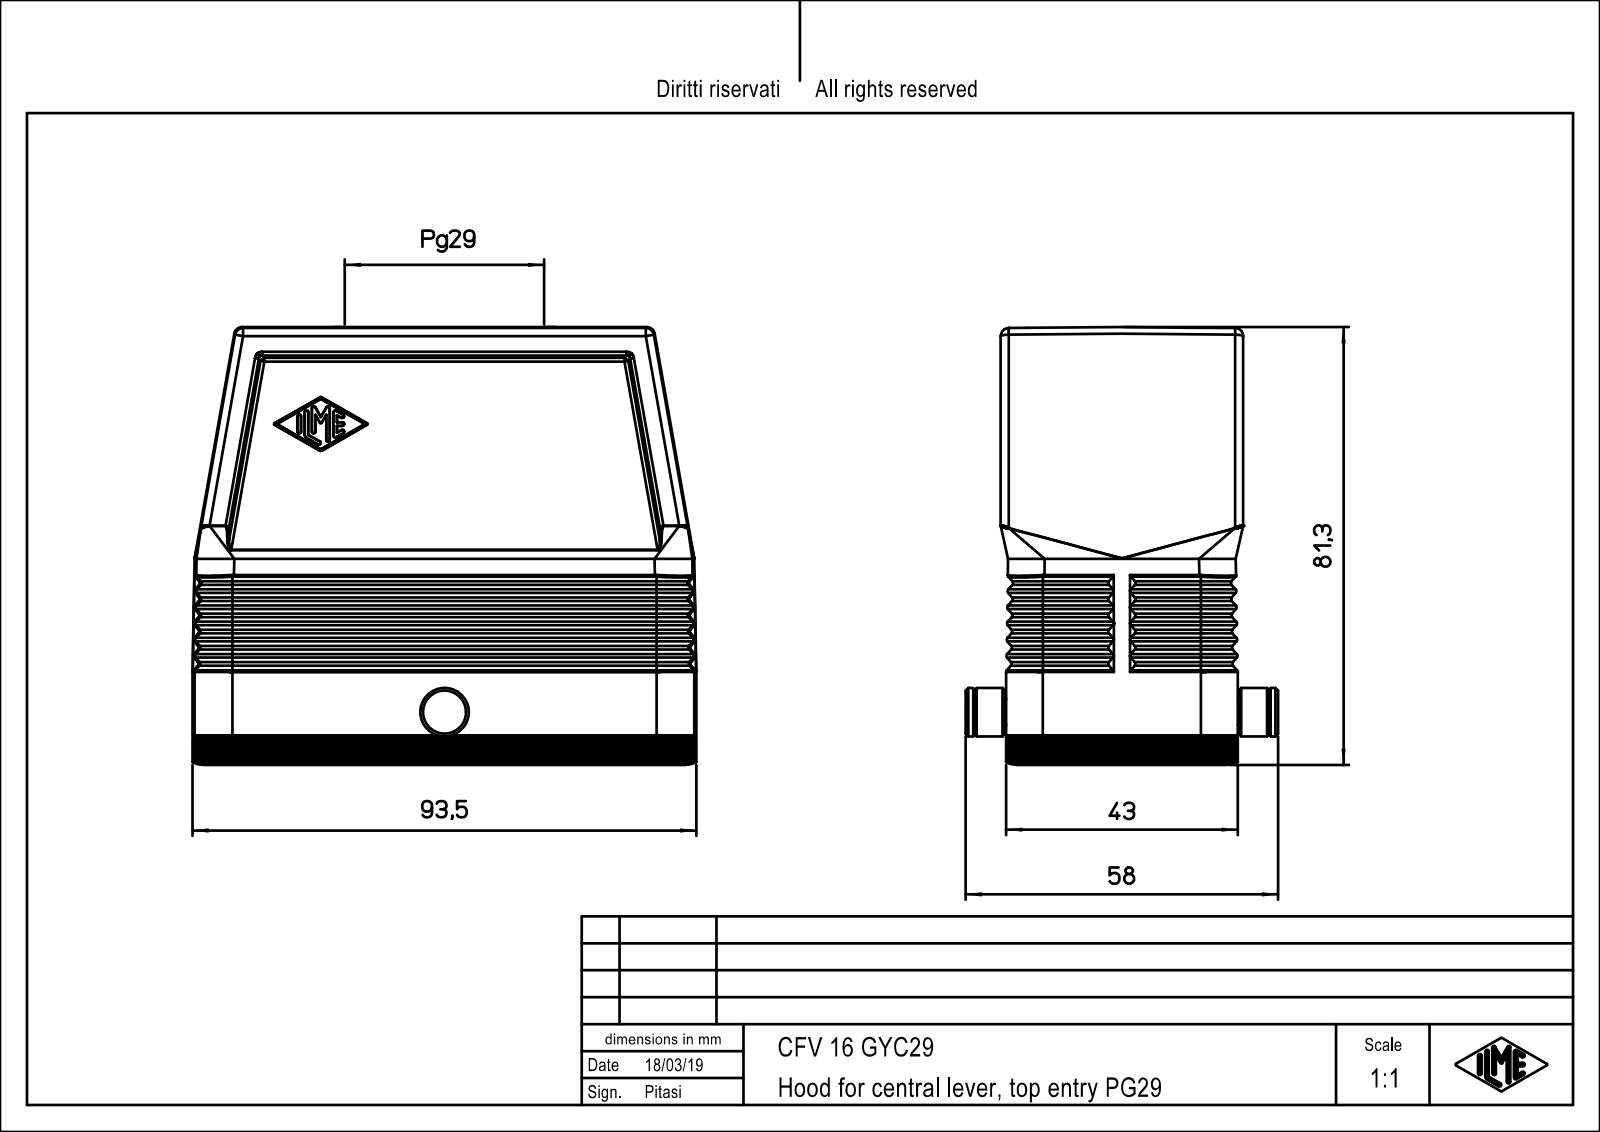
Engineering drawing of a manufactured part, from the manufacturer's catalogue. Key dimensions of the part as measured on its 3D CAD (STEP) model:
Part name (STEP PRODUCT): CFV_16_GYC29
STEP written by: PTC Creo Elements/Direct Modeling 19.0E 27-Jun-2016 (C) Parametric Technology GmbH (AUTOMOTIVE_DESIGN)
Units: millimetres
Bodies: 1 solid, 580 faces (226 planar, 174 cylindrical, 180 other)
Overall size (bounding box): 93.5 × 81.25 × 58
Volume: 101 121 mm³ · Surface area: 46 962 mm²
Round holes (diameter × count): ⌀36.24 ×1
Round bosses / shafts (diameter × count): ⌀9 ×1, ⌀4.8 ×1
Partial cylindrical surfaces — rounded edges, fillets, slot ends (radius × count): R0.5 ×84, R1 ×16, R7 ×12, R1.5 ×10, R3 ×8, R3.5 ×4, R4 ×4, R4.2 ×4
Main face-to-face distances: 43, 4, 1.01, 2, 7, 6, 44, 1, 39, 5
